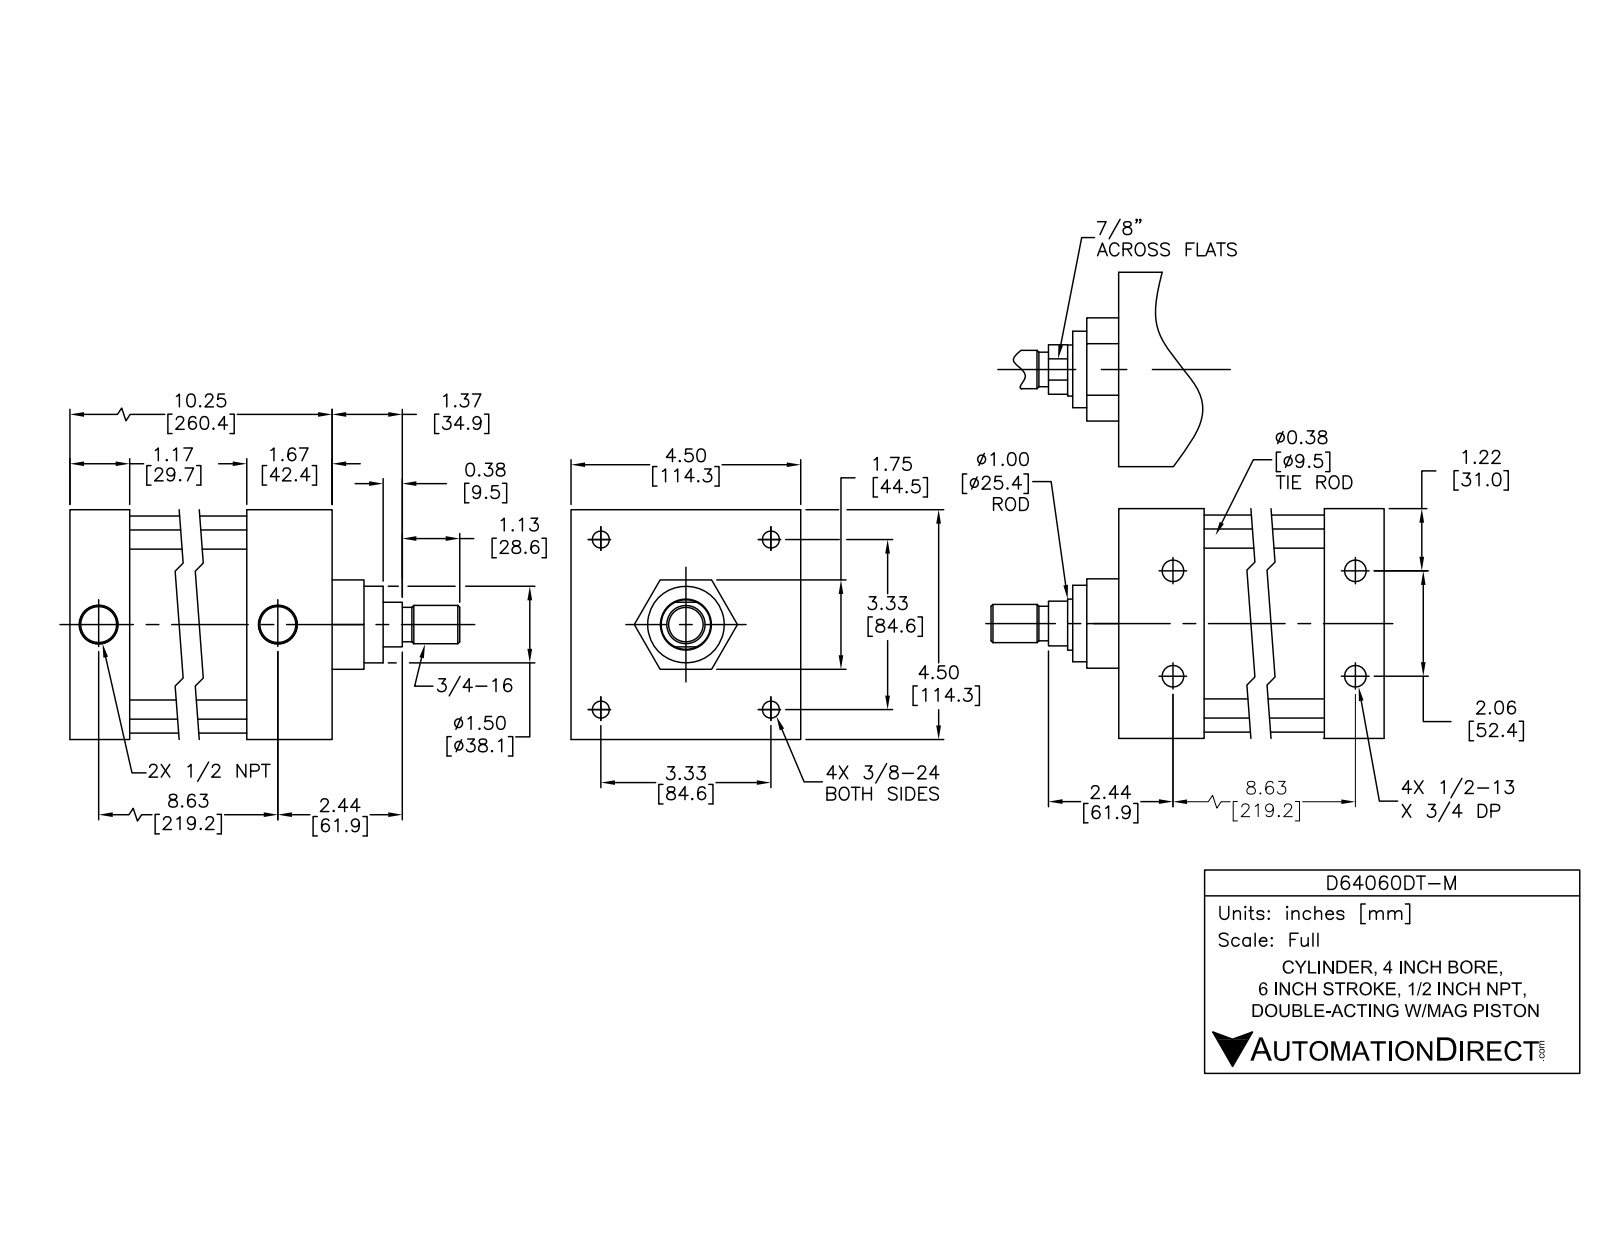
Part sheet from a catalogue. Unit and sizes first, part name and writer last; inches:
Units: inches
Overall size (bounding box): 12.745 × 4.5 × 4.5
Round holes (diameter × count): ⌀0.33 ×4, ⌀0.406 ×4, ⌀0.417 ×4, ⌀0.625 ×4, ⌀0.5 ×2, ⌀0.766 ×2, ⌀1 ×1, ⌀1.003 ×1, ⌀4 ×1
Round bosses / shafts (diameter × count): ⌀0.609 ×4, ⌀0.375 ×4, ⌀0.34 ×4, ⌀4.25 ×1, ⌀3.997 ×1, ⌀1.75 ×1, ⌀0.997 ×1, ⌀0.97 ×1
Partial cylindrical surfaces — rounded edges, fillets, slot ends (radius × count): R0.45 ×4
Main face-to-face distances: 4.5, 0.08, 7.326, 10.246, 1.75, 8.997, 1.249, 7.751, 1.246, 2.495
Hole centre spacings: 2.349, 3.322, 8.683, 8.622, 1.031, 1.031, 2.062, 4.698
Volume: 93.93 in³ · Surface area: 490.3 in²
Bodies: 12 solids, 303 faces (99 planar, 114 cylindrical, 90 other)
Part name (STEP PRODUCT): D64060DT-M; D64060DT-M BODY; D64060DT-M PISTON
STEP written by: SolidWorks 2015 (AUTOMOTIVE_DESIGN)
